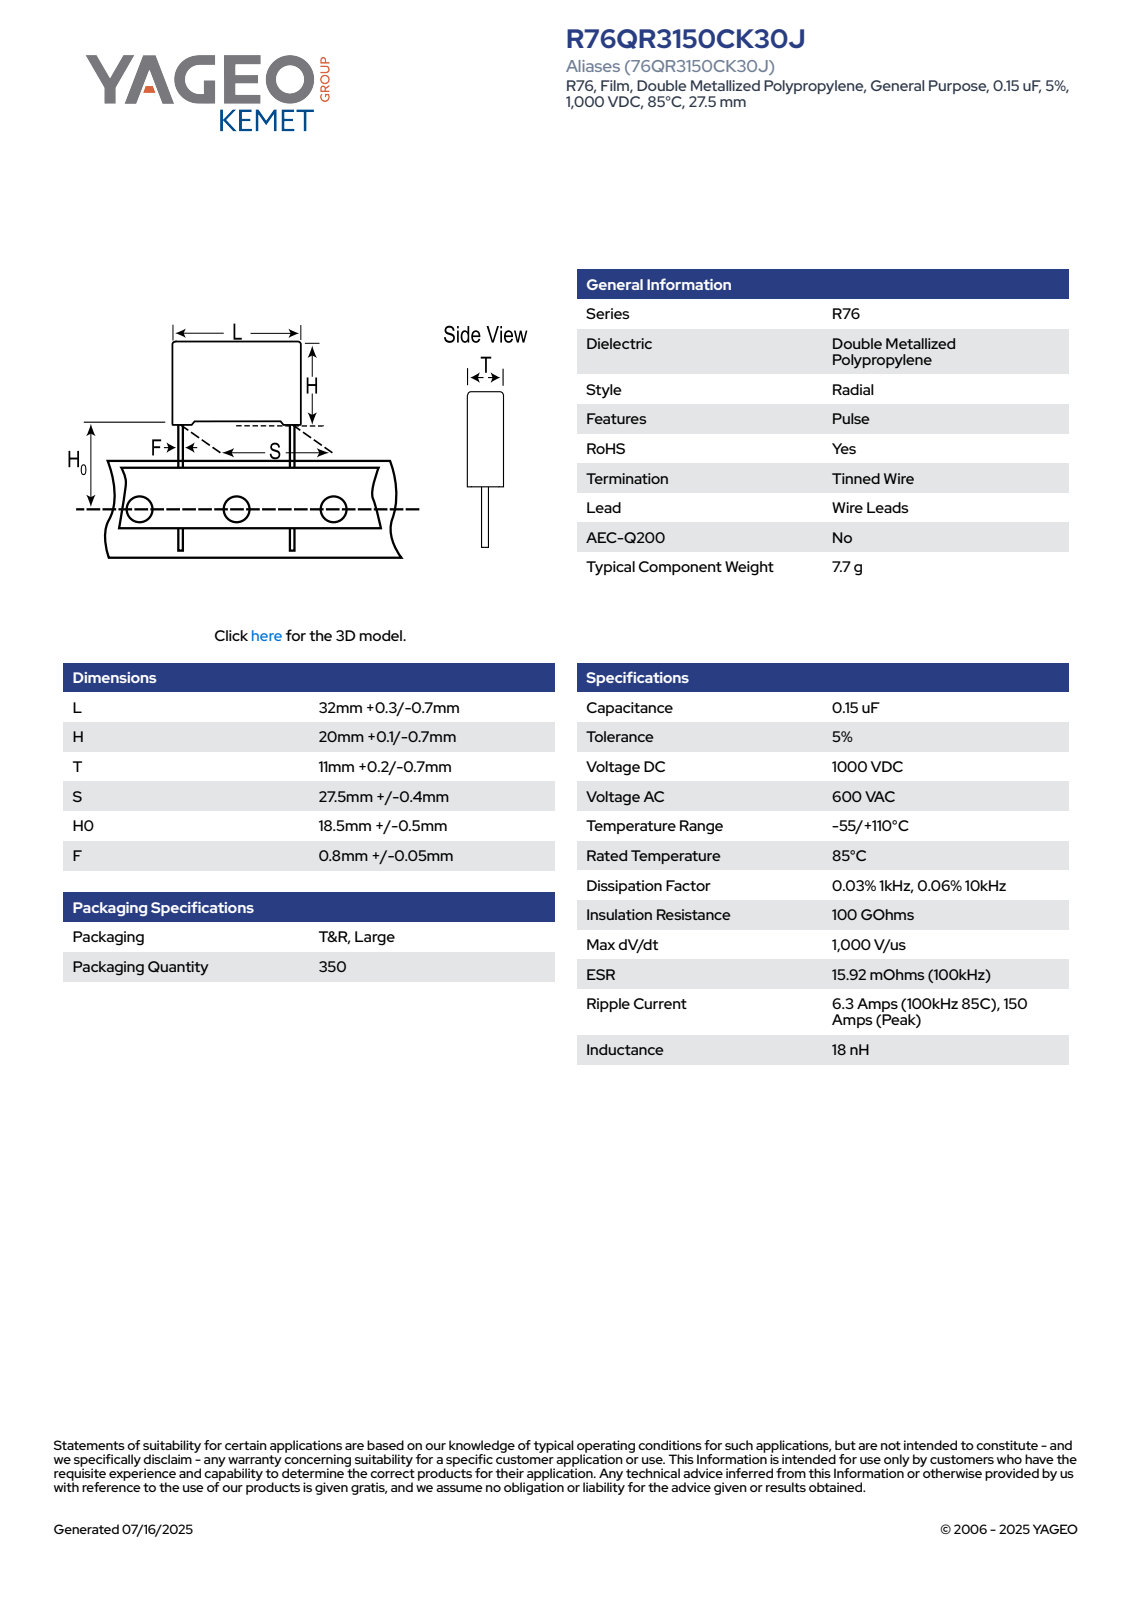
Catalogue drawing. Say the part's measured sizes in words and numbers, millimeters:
The part is named "CFR_RB2_32X20X11_L32.3H20.1T11.2S27.5H019F0.85". Its 3-D file was written by "SolidWorks 2020 (AUTOMOTIVE_DESIGN)". It is 4 solids with 85 faces: 77 planar, 8 cylindrical and 0 other. Overall it measures 39.1 by 32.3 by 11.21 millimeters. Its volume is 7 050 cubic millimeters and its surface area 2 631 square millimeters. Round bosses or shafts: 2 of diameter 0.85. Partial cylindrical surfaces (rounded edges, fillets, slot ends): 4 of radius 0.5. The main face-to-face distances are 11.2, 19.35, 32.3, 19.41, 0.69, 0.75, 20.1, 1.08, 11.21, 31.22.
